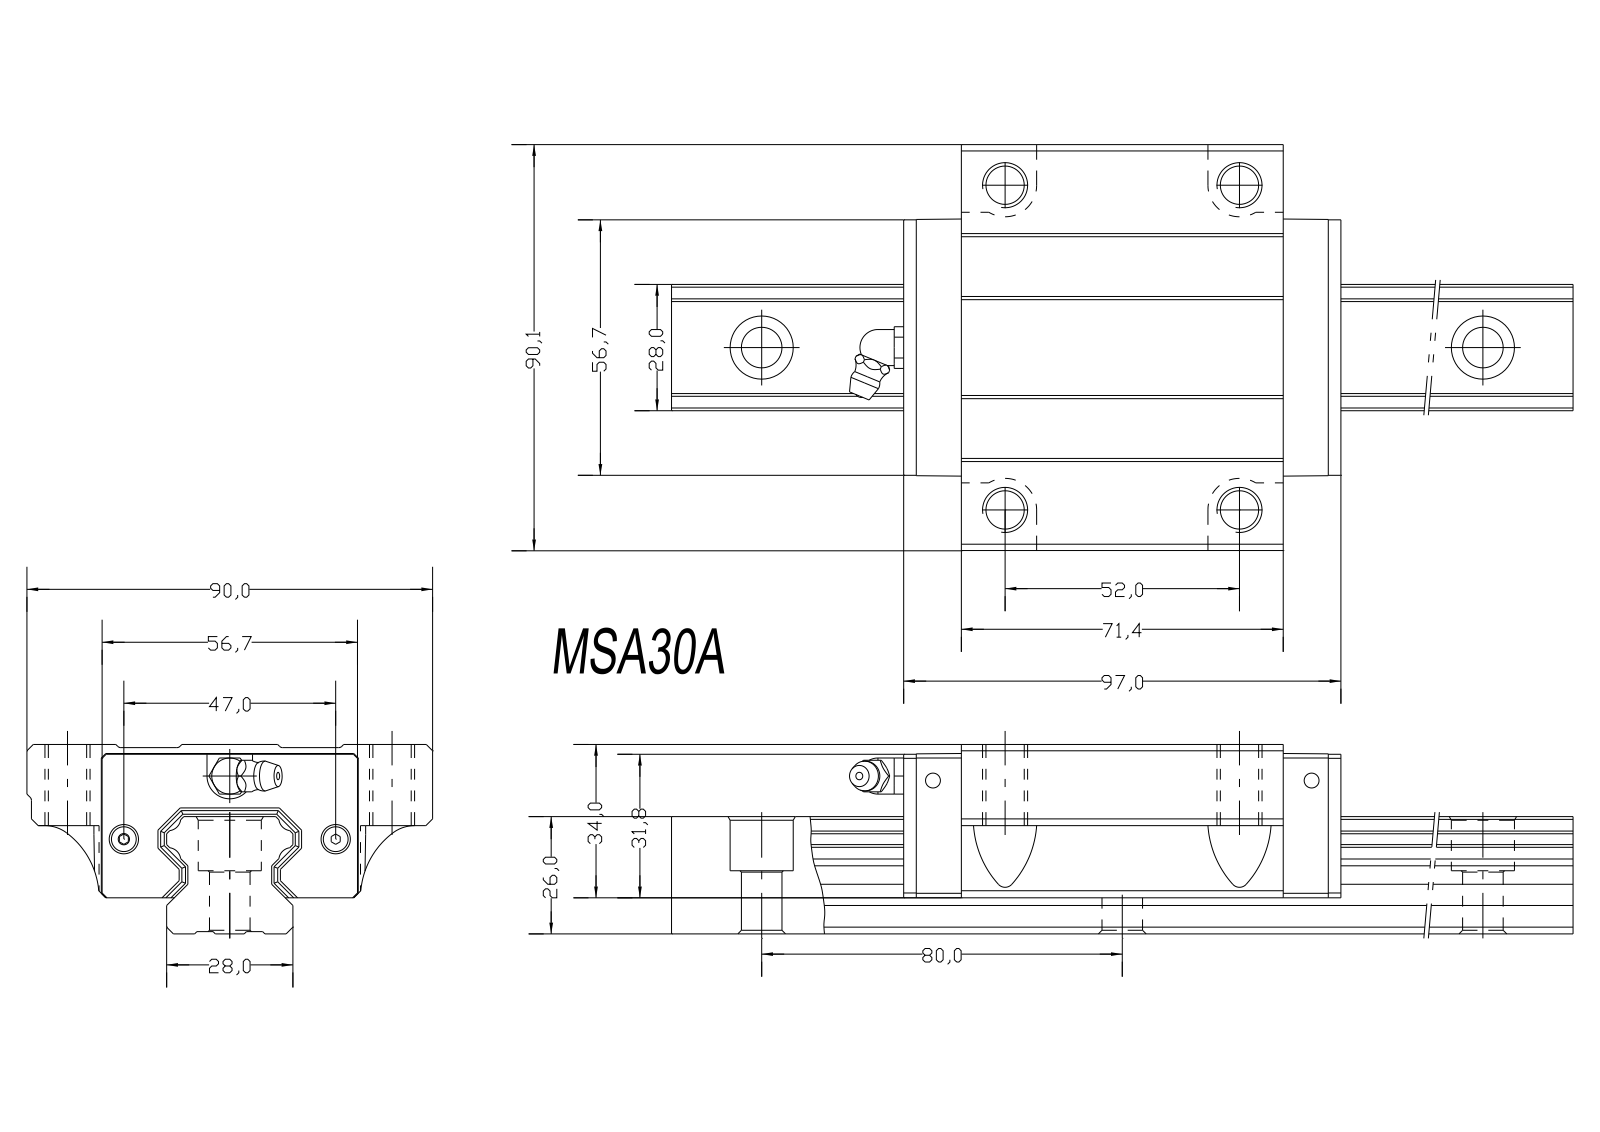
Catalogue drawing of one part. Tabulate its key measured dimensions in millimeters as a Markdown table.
| quantity | value |
| --- | --- |
| STEP written by | Kubotek KeyCreator V6.5.2 (0407) (CONFIG_CONTROL_DESIGN) |
| units | millimeters |
| bodies | 3 solids, 236 faces (146 planar, 73 cylindrical, 17 other) |
| overall size | 280 × 90 × 42 |
| volume | 345 580 mm³ |
| surface area | 68 536 mm² |
| round holes (diameter × count) | 9 × 4, 10 × 4, 14 × 4, 6.5 × 3, 3.25 × 2 |
| round bosses / shafts (diameter × count) | 8 × 1 |
| partial cylindrical surfaces (radius × count) | 3.1 × 4, 7 × 4, 8 × 2, 18 × 2, 1 × 1, 5.05 × 1 |
| main face-to-face distances | 16, 26, 42, 18, 8, 34, 4.77, 23.23, 0.7, 7.5 |
| hole center spacings | 38.63, 75.18, 100.66, 150.37, 80, 27.35, 52, 72 |
